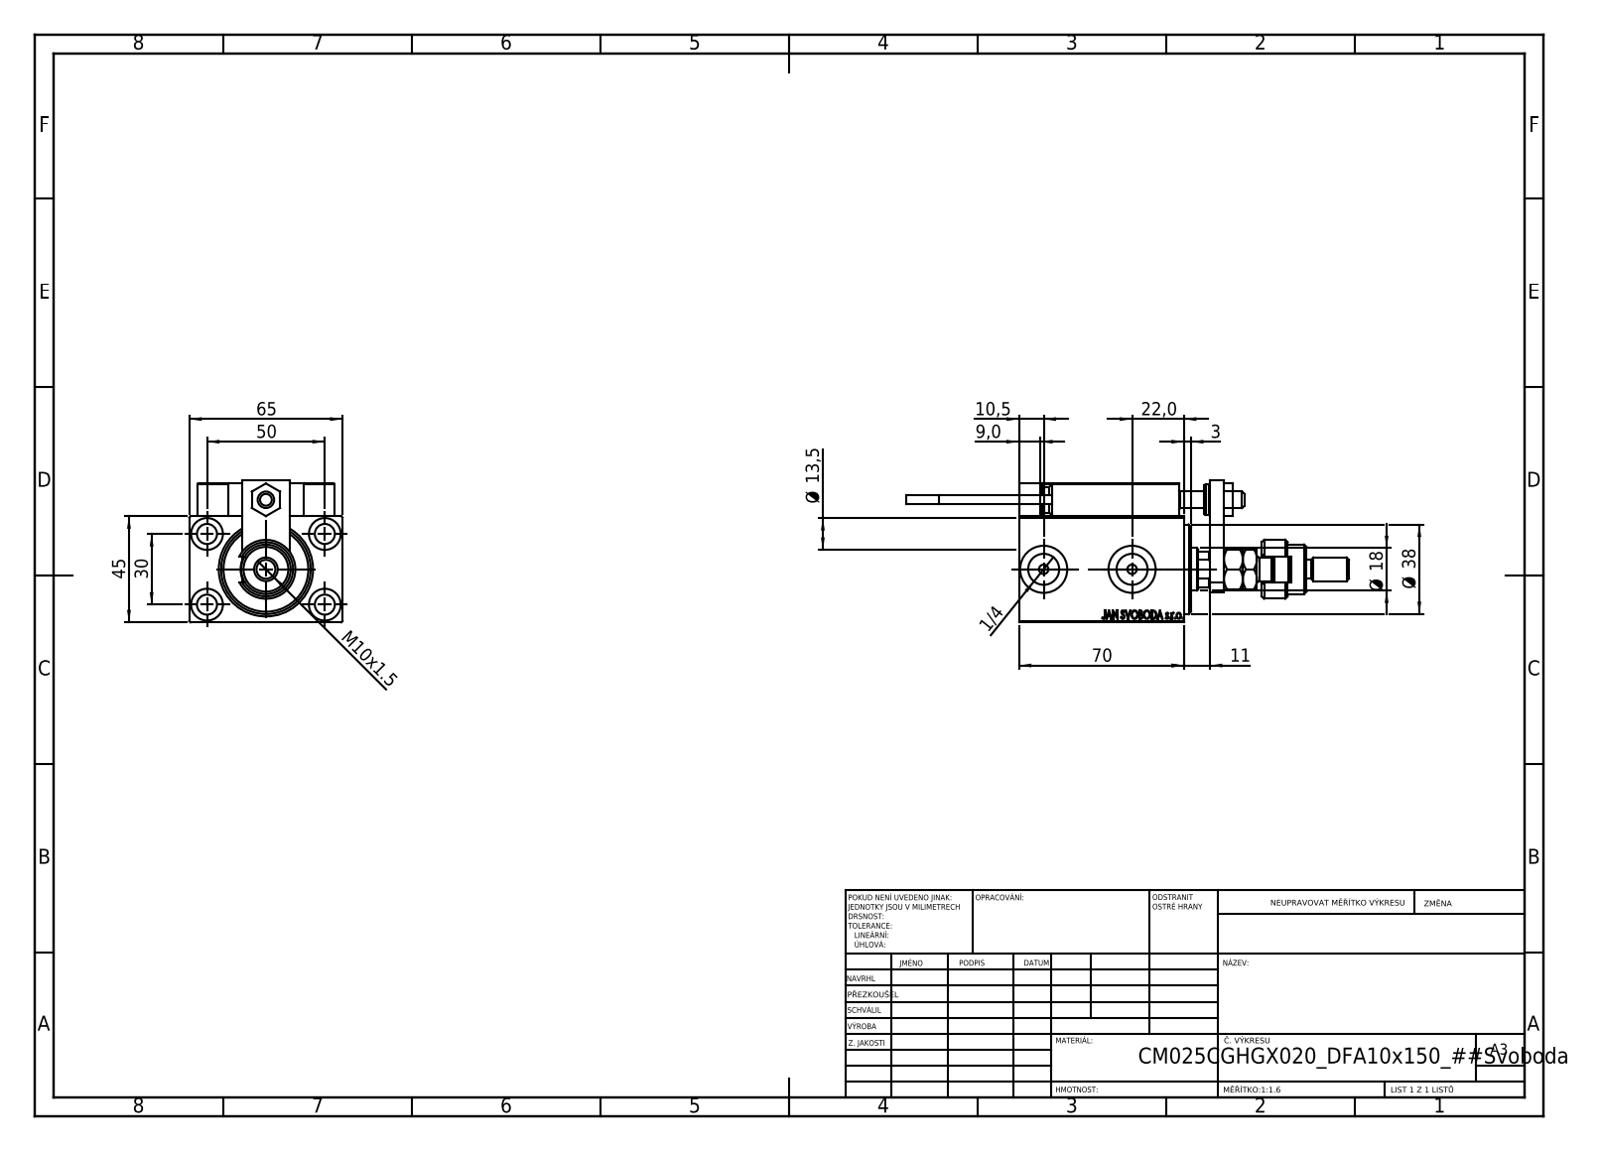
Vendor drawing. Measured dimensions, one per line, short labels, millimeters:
name: X_Y_DFA; MFA; Block; MAGNET (+7 more)
written by: SolidWorks 2019 (CONFIG_CONTROL_DESIGN)
unit: mm
bodies: 25 solids, 1367 faces (588 planar, 201 cylindrical, 578 other)
size: 188 × 65 × 60.5
volume: 234 905 mm³; area: 74 636 mm²
holes: 6× ⌀4, 5× ⌀8, 5× ⌀8.5, 4× ⌀3.2, 4× ⌀13.5, 2× ⌀5, 2× ⌀13.16, 2× ⌀20, 1× ⌀7, 1× ⌀14.5, 1× ⌀18, 1× ⌀21.5
bosses: 2× ⌀5, 2× ⌀3.8, 1× ⌀25, 1× ⌀21, 1× ⌀16, 1× ⌀13, 1× ⌀11, 1× ⌀10
rounds: 30× R0.3, 2× R3, 1× R5.5, 1× R8.5, 1× R8.75
face distances: 45, 59, 14, 65, 6, 3, 19, 7, 5, 13
hole spacings: 29.15, 11.37, 20, 22.09, 28.9, 29.59, 29.69, 30
